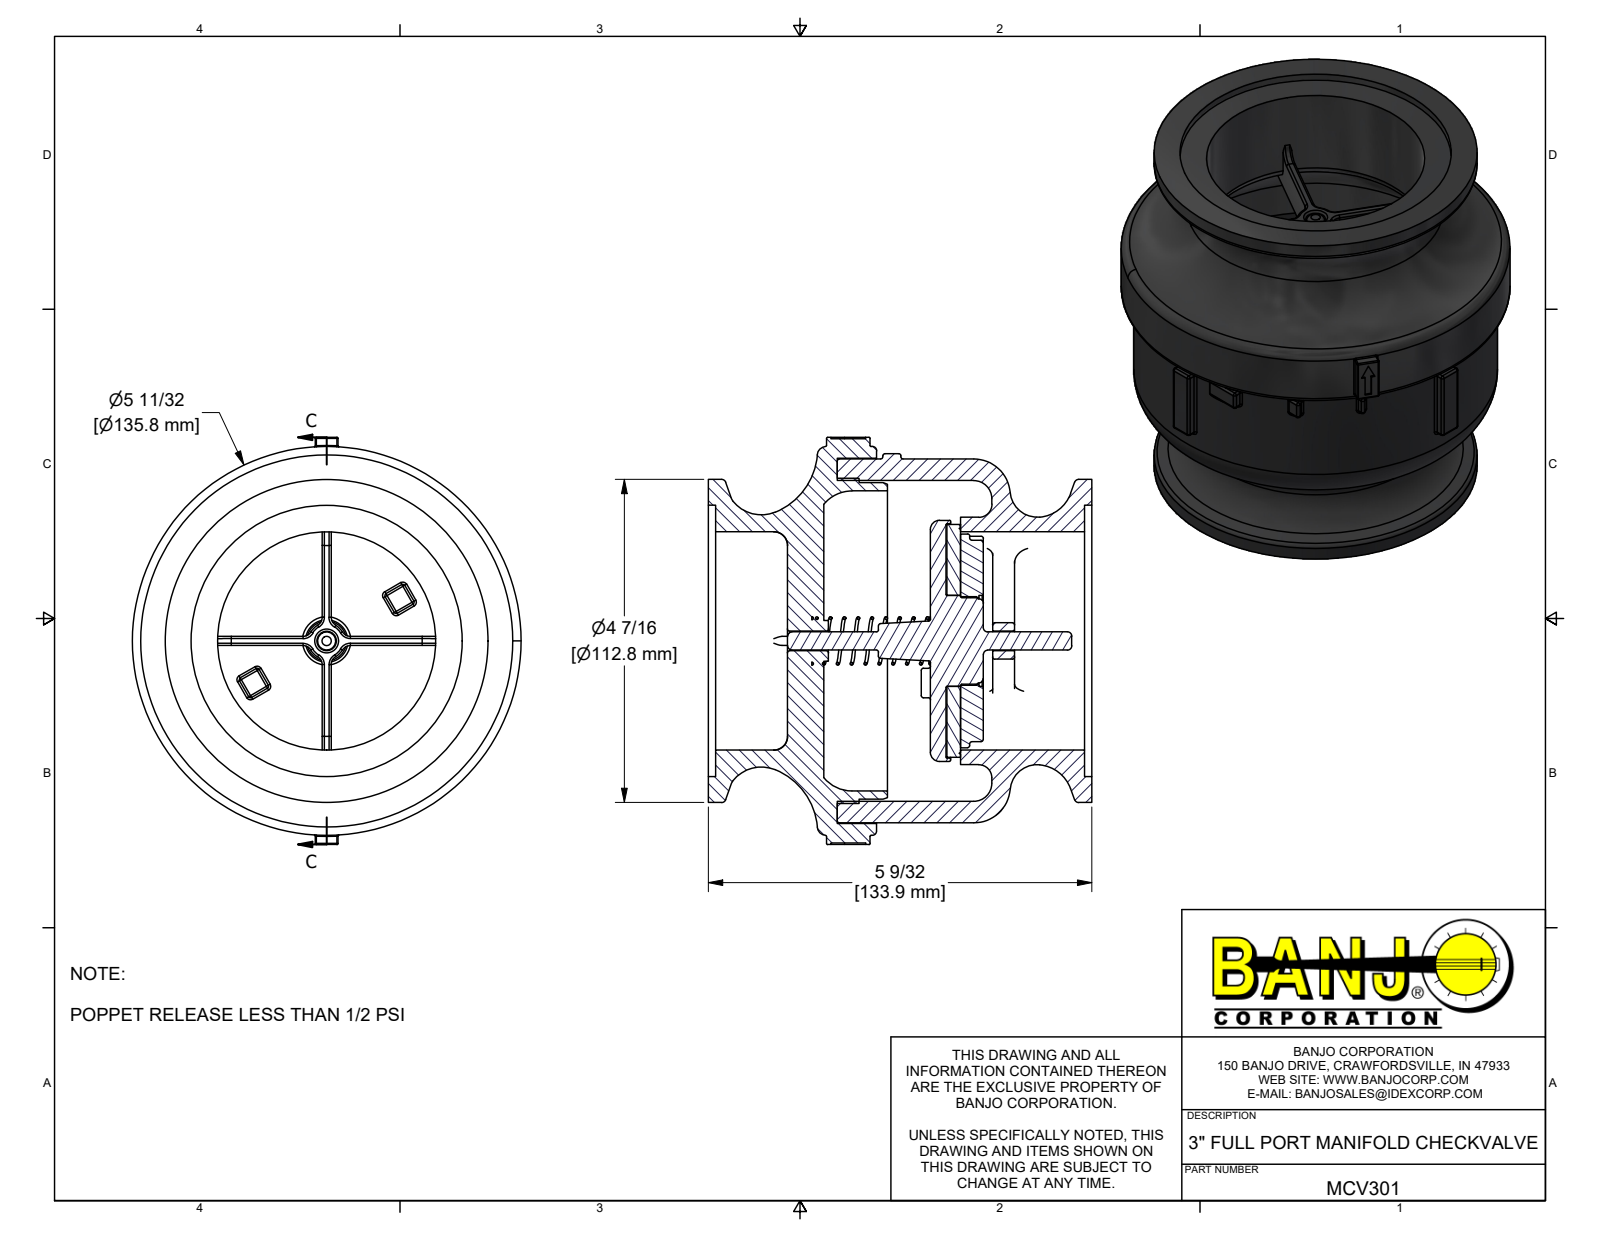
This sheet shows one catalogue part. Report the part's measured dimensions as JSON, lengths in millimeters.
{"part_name": "MCV301; MCV30054; MCV30054X; MCV30056 (+6 more)", "step_written_by": "Autodesk Inventor 2022 (AUTOMOTIVE_DESIGN)", "units": "millimeters", "bodies": {"solids": 6, "faces": 643, "planar": 148, "cylindrical": 217, "other": 278}, "overall_size": [135.8, 135.8, 133.9], "volume_mm3": 597800, "surface_area_mm2": 199300, "round_holes": [[6.9, 1], [30.2, 1], [31.8, 1], [76.2, 1], [81.8, 1], [94.7, 1], [104.8, 1], [112, 1], [127.5, 1]], "round_bosses_or_shafts": [[135.8, 1], [127, 1], [113.5, 1], [112.8, 1], [110.5, 1], [86.4, 1], [84.2, 1], [81.3, 1]], "partial_cylinders_radius": [[0.8, 113], [0.4, 20], [3.2, 12], [1.5, 8], [6.4, 1], [7.1, 1], [64.3, 1]], "face_to_face_distances": [43.1, 2.5, 131.4, 32.5, 4.7, 10.5, 5.8, 38.3, 5.1, 0.3]}
